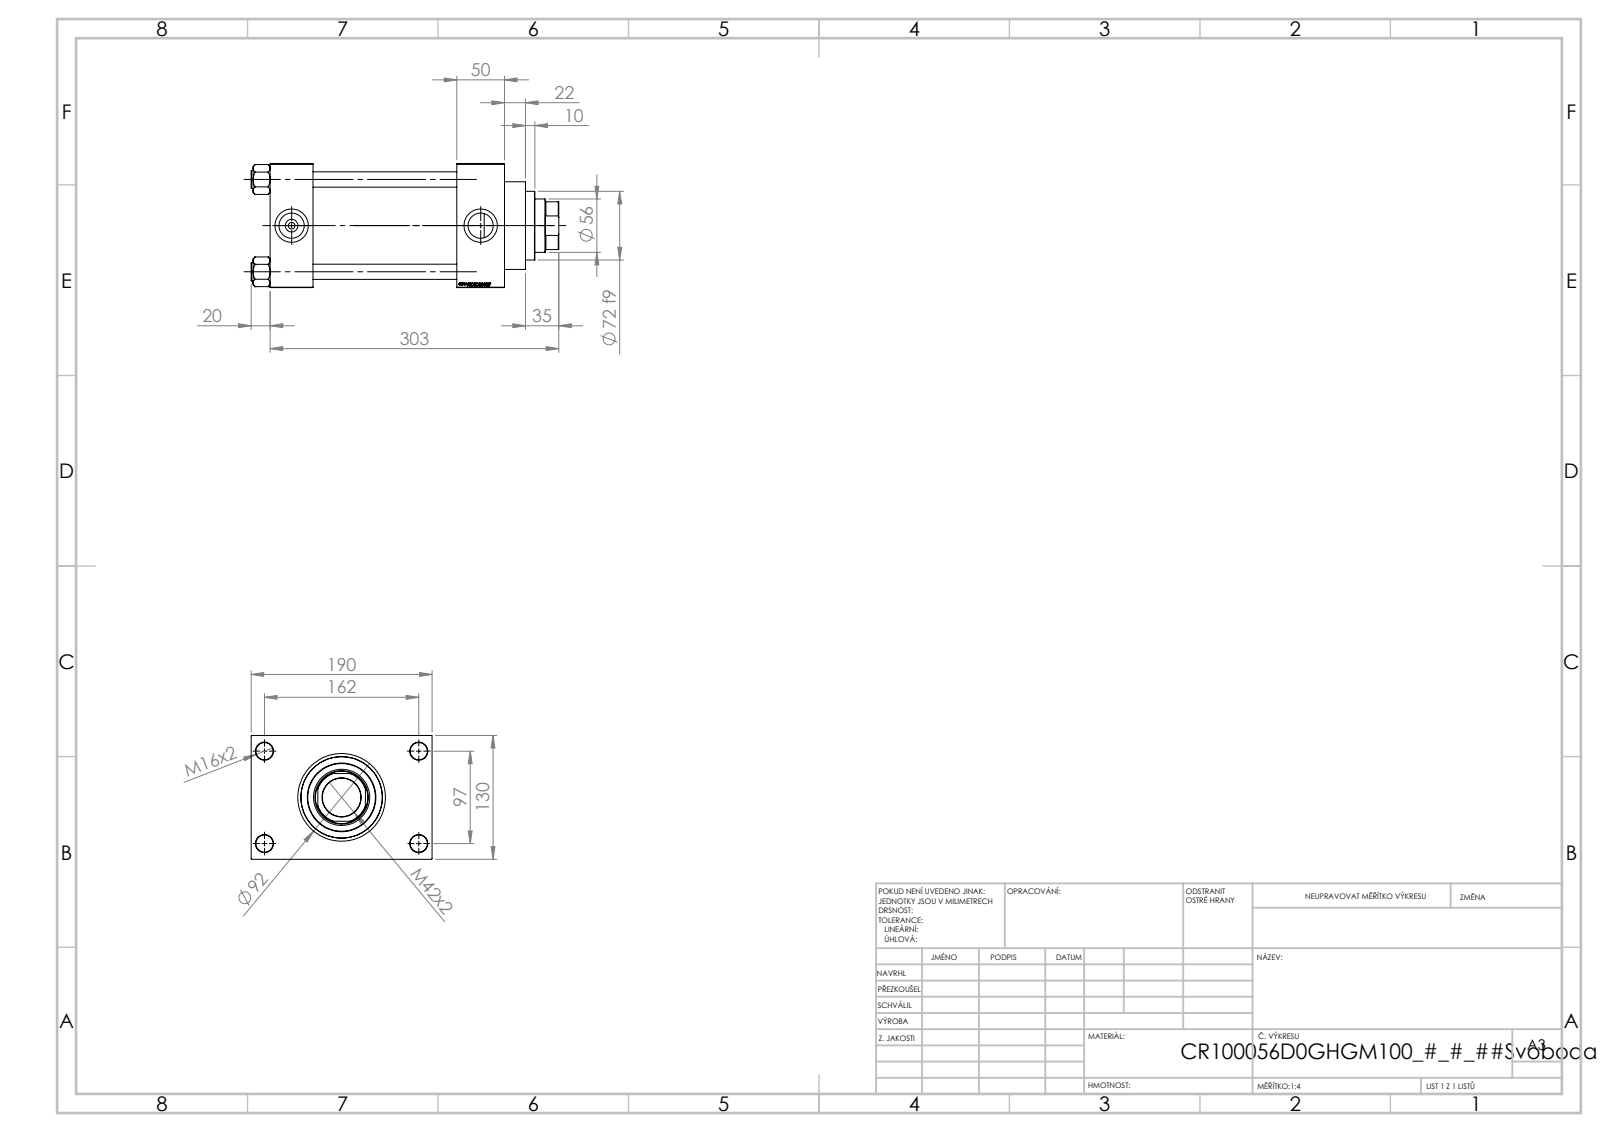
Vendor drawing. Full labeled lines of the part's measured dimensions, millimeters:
Part name (STEP PRODUCT): V215CR_D_Body; V215CR_VCP_D; NUT_M5_D; V215CR_D_TYCINKA (+1 more)
STEP written by: SolidWorks 2019 (CONFIG_CONTROL_DESIGN)
Units: millimetres
Bodies: 11 solids, 1151 faces (545 planar, 88 cylindrical, 518 other)
Overall size (bounding box): 323 × 190 × 130
Volume: 2 967 000 mm³ · Surface area: 444 296 mm²
Round holes (diameter × count): ⌀16 ×4, ⌀18 ×4, ⌀7 ×2, ⌀26.44 ×2, ⌀35 ×2, ⌀40.5 ×1, ⌀56 ×1, ⌀59 ×1, ⌀76 ×1, ⌀85.5 ×1, ⌀100 ×1
Round bosses / shafts (diameter × count): ⌀19 ×4, ⌀106 ×1, ⌀92 ×1, ⌀72 ×1
Partial cylindrical surfaces — rounded edges, fillets, slot ends (radius × count): R27 ×1
Main face-to-face distances: 130, 50, 45, 196, 151, 246, 201, 30, 160, 190
Hole centre spacings: 32.55, 68.52, 94.41, 96.9, 102.27, 129.45, 161.73, 97
